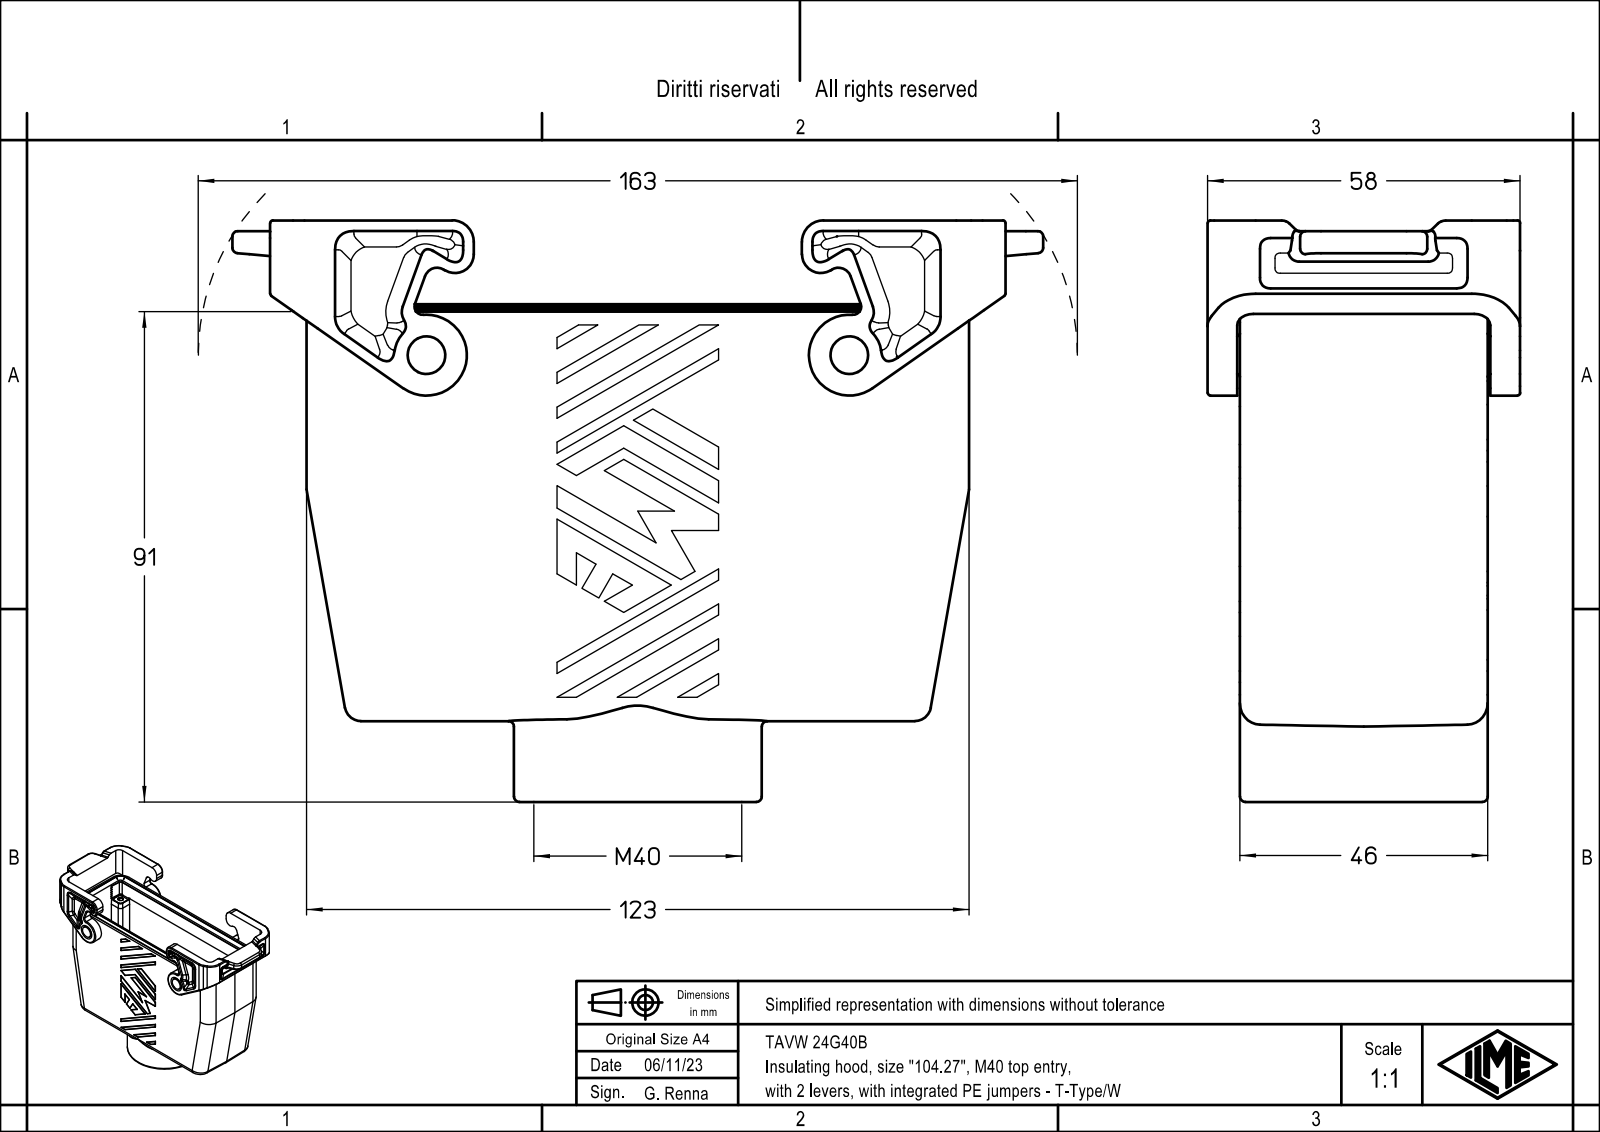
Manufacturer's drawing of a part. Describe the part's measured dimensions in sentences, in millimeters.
The part is named "TAVW 24G40B". Its 3-D file was written by "Creo Elements/Direct Modeling 20.1B 02-Apr-2019 (C) Parametric Technology GmbH (AUTOMOTIVE_DESIGN)". It is 1 solid with 754 faces: 374 planar, 318 cylindrical and 62 other. Overall it measures 150.5 by 107.9 by 58 millimeters. Its volume is 180 382 cubic millimeters and its surface area 75 685 square millimeters. Round holes: 4 of diameter 3.5, 1 of diameter 34, 1 of diameter 38.6. Round bosses or shafts: 2 of diameter 7, 1 of diameter 46. Partial cylindrical surfaces (rounded edges, fillets, slot ends): 88 of radius 0.15, 20 of radius 2, 20 of radius 3, 18 of radius 1.5, 16 of radius 1, 12 of radius 1.3, 8 of radius 6, 8 of radius 7. The main face-to-face distances are 5.4, 40.6, 35.2, 46, 5.9, 0.5, 41.1, 46.5, 34.8, 6.6. The hole center spacings are 53.72, 27, 104, 107.45.
